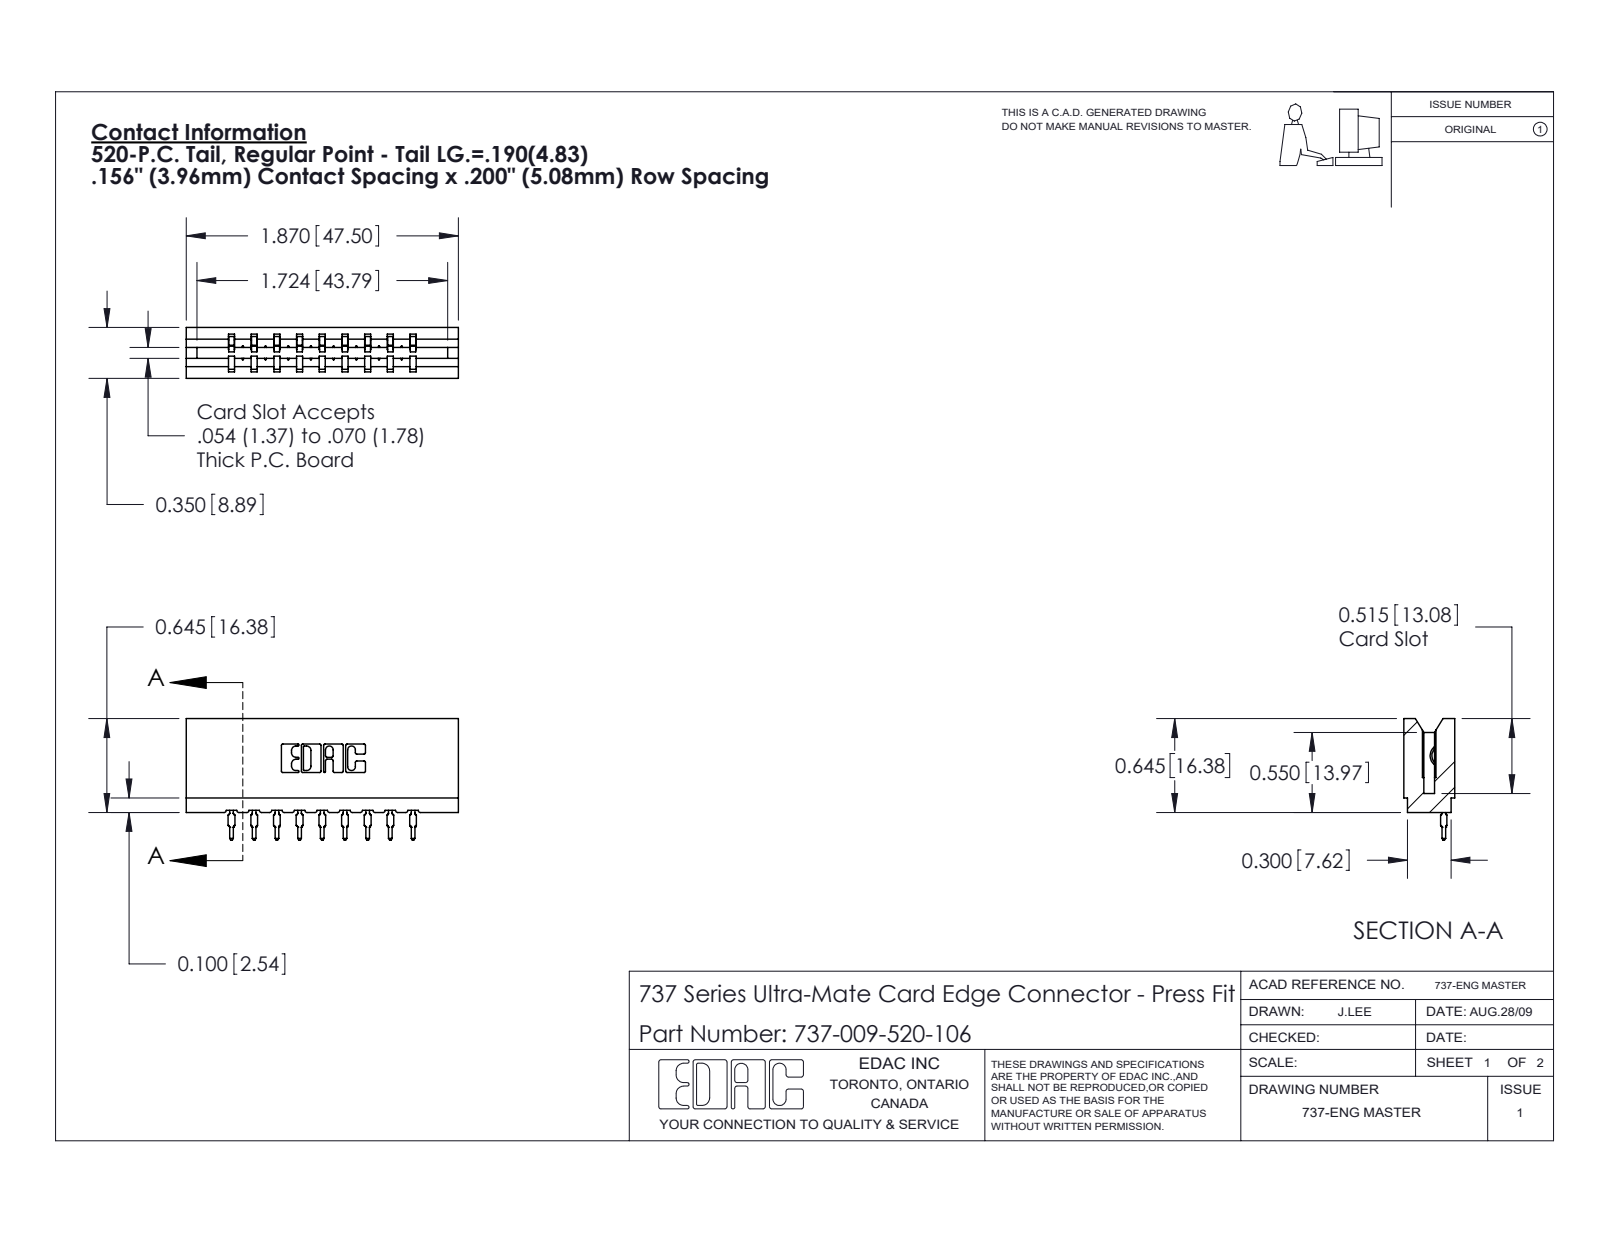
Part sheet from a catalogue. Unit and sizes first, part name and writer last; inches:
Units: inches
Overall size (bounding box): 1.87 × 0.836 × 0.35
Partial cylindrical surfaces — rounded edges, fillets, slot ends (radius × count): R0.01 ×22, R0.015 ×18, R0.021 ×18, R0.007 ×6, R0.031 ×6, R0.005 ×4, R0.011 ×4, R0.026 ×3
Main face-to-face distances: 0.156, 0.138, 0.212, 0.624, 0.35, 0.312, 0.468, 0.354, 0.198, 0.78
Volume: 0.292 in³ · Surface area: 8.941 in²
Bodies: 10 solids, 1112 faces (667 planar, 211 cylindrical, 234 other)
Part name (STEP PRODUCT): 737-009-520-106; 745-292-001_520; 737 Part_Insulator Option - 06
STEP written by: SolidWorks 2020 (CONFIG_CONTROL_DESIGN)
